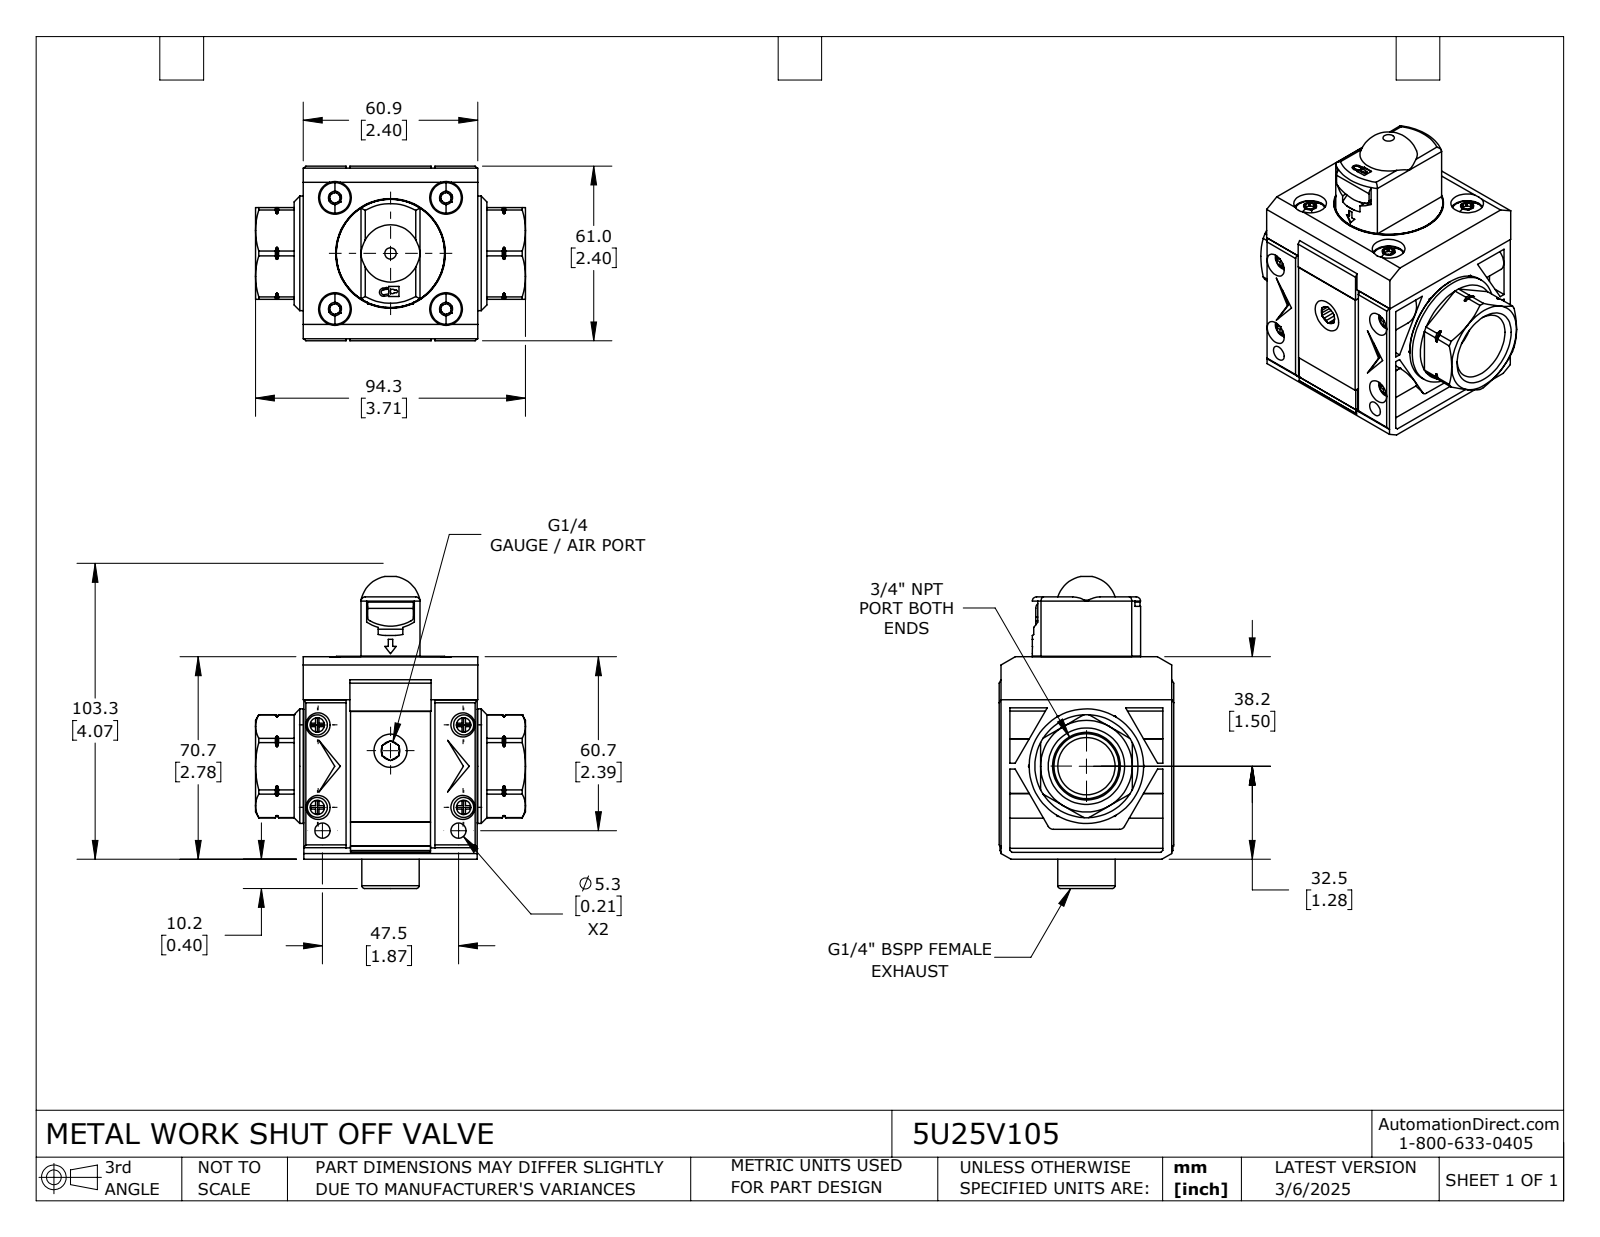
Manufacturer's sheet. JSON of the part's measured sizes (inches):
{"part_name": "5U25V105", "step_written_by": "SolidWorks 2024 (CONFIG_CONTROL_DESIGN)", "units": "inches", "bodies": {"solids": 13, "faces": 912, "planar": 450, "cylindrical": 250, "other": 212}, "overall_size": [4.288, 3.713, 2.402], "volume_in3": 16.07, "surface_area_in2": 119.6, "round_holes": [[0.128, 4], [0.165, 4], [0.331, 4], [0.449, 4], [0.209, 2], [0.451, 1], [0.457, 1], [0.787, 1], [1.508, 1]], "round_bosses_or_shafts": [[0.276, 4], [0.189, 4], [0.15, 4], [1.575, 1], [1.496, 1], [1.378, 1], [1.248, 1], [1.035, 1]], "partial_cylinders_radius": [[0.011, 24], [0.059, 4], [0.069, 4], [0.191, 4], [0.079, 2], [0.242, 2], [0.591, 2], [0.018, 1]], "face_to_face_distances": [0.094, 2.39, 2.193, 2.098, 2.402, 0.299, 0.028, 1.799, 2.319, 2.382], "hole_center_spacings": [1.08, 1.528, 0.325, 1.057, 1.134, 1.265, 1.443, 1.454]}
